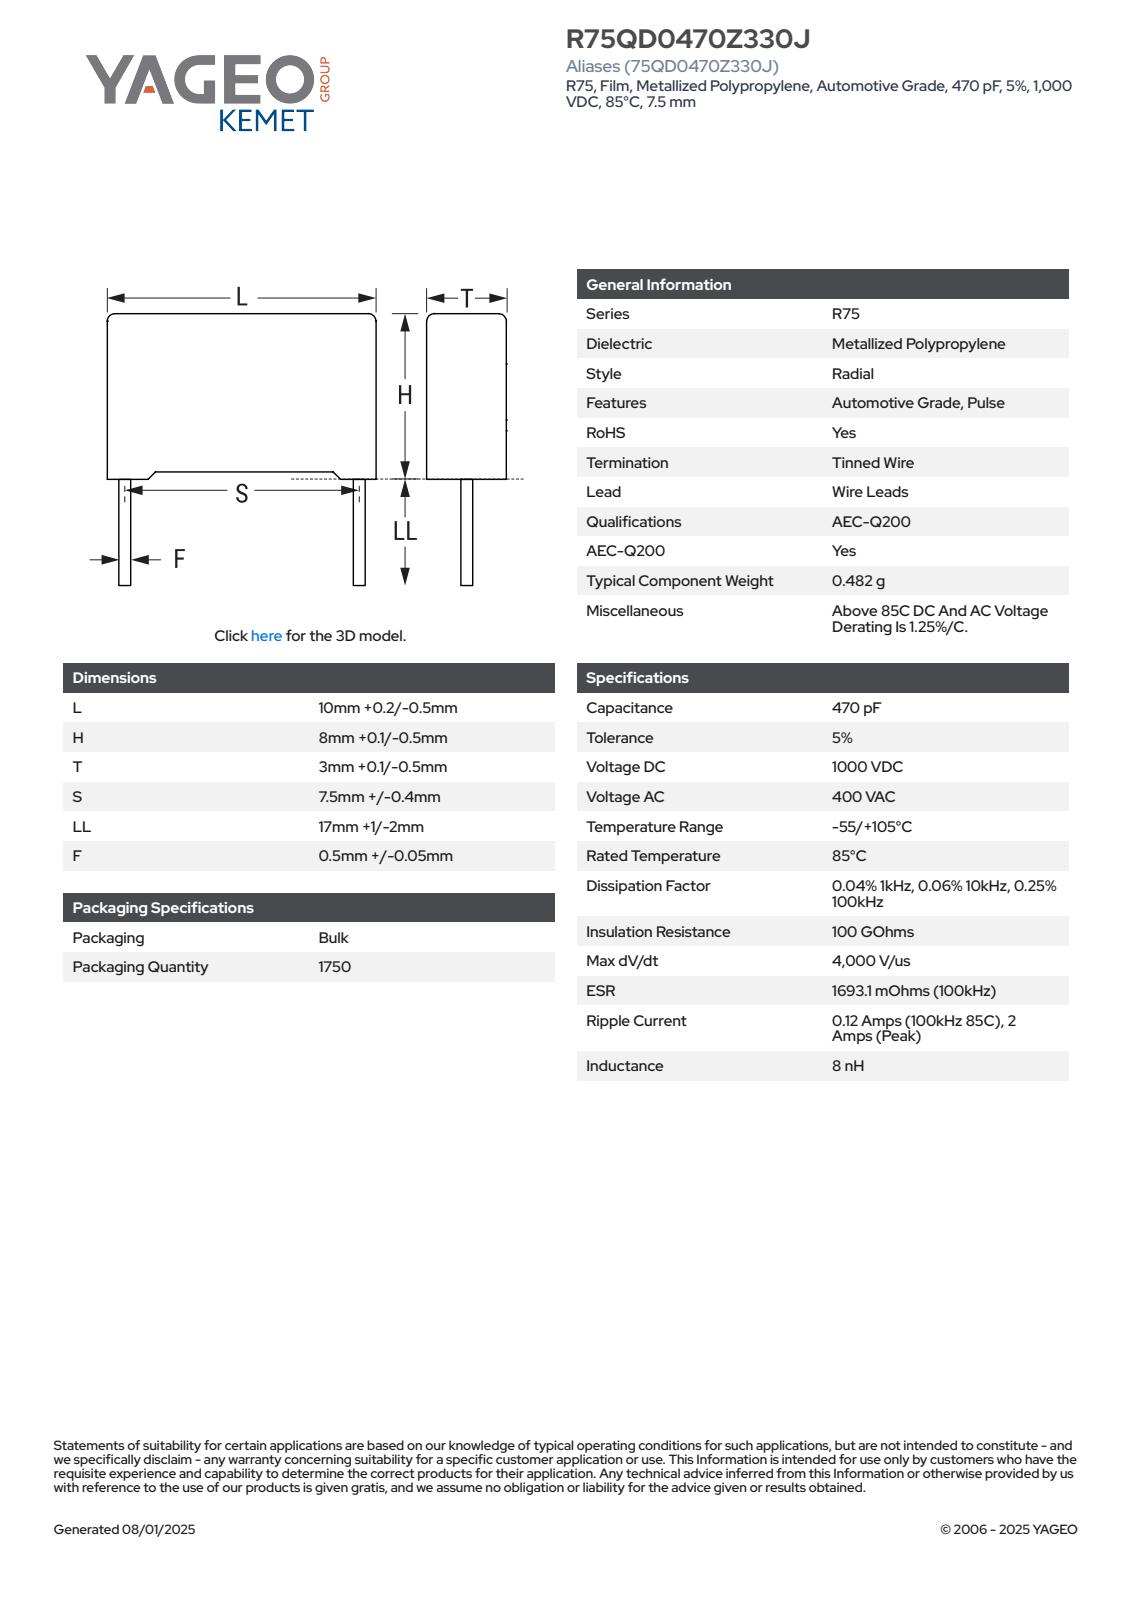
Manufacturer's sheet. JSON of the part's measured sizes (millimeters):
{"part_name": "CFR_RB2_10X8X3_L10.2H8.1T3.1S7.5LL18F0.55", "step_written_by": "SolidWorks 2021 (AUTOMOTIVE_DESIGN)", "units": "millimeters", "bodies": {"solids": 4, "faces": 85, "planar": 77, "cylindrical": 8, "other": 0}, "overall_size": [26.1, 10.2, 3.1], "volume_mm3": 246, "surface_area_mm2": 359, "round_bosses_or_shafts": [[0.55, 2]], "partial_cylinders_radius": [[0.5, 4]], "face_to_face_distances": [3.1, 10.2, 7.35, 0.34, 2.76, 2.42, 0.75, 8.1, 9.86, 0.47]}
